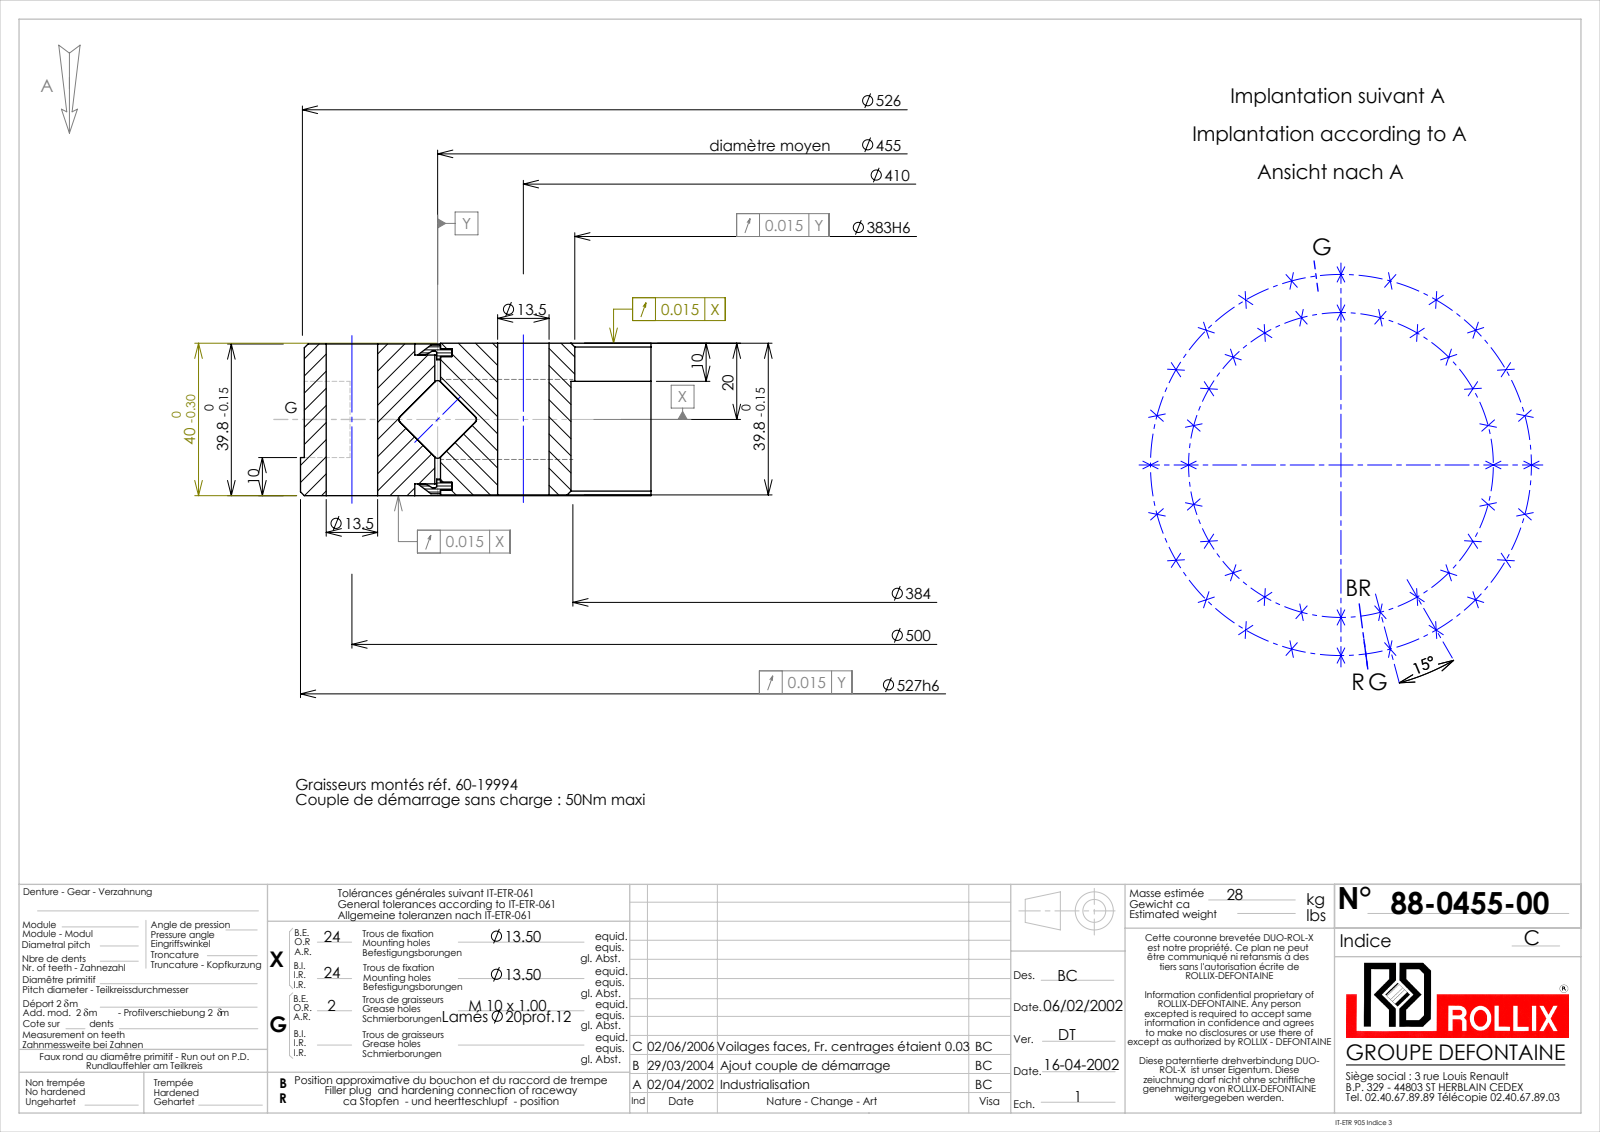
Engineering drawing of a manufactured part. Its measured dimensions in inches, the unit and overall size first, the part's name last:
Units: inches
Overall size (bounding box): 20.748 × 20.748 × 1.575
Round holes (diameter × count): ⌀0.531 ×48, ⌀0.354 ×2, ⌀0.787 ×2, ⌀15.079 ×1, ⌀15.118 ×1, ⌀17.618 ×1, ⌀17.854 ×1, ⌀17.972 ×1, ⌀18.386 ×1
Round bosses / shafts (diameter × count): ⌀0.394 ×2, ⌀20.748 ×1, ⌀20.709 ×1, ⌀17.933 ×1, ⌀0.591 ×1
Main face-to-face distances: 1.567, 1.559, 1.575, 0.122, 1.453, 0.114, 1.445, 0.059, 1.516, 0.051
Hole centre spacings: 9.843, 11.983, 18.187, 5.095, 2.57, 7.533, 15.617, 19.517
Volume: 207.2 in³ · Surface area: 945.4 in²
Bodies: 7 solids, 255 faces (46 planar, 154 cylindrical, 55 other)
Part name (STEP PRODUCT): 88-0455-00
STEP written by: SolidWorks 2016 (CONFIG_CONTROL_DESIGN)
